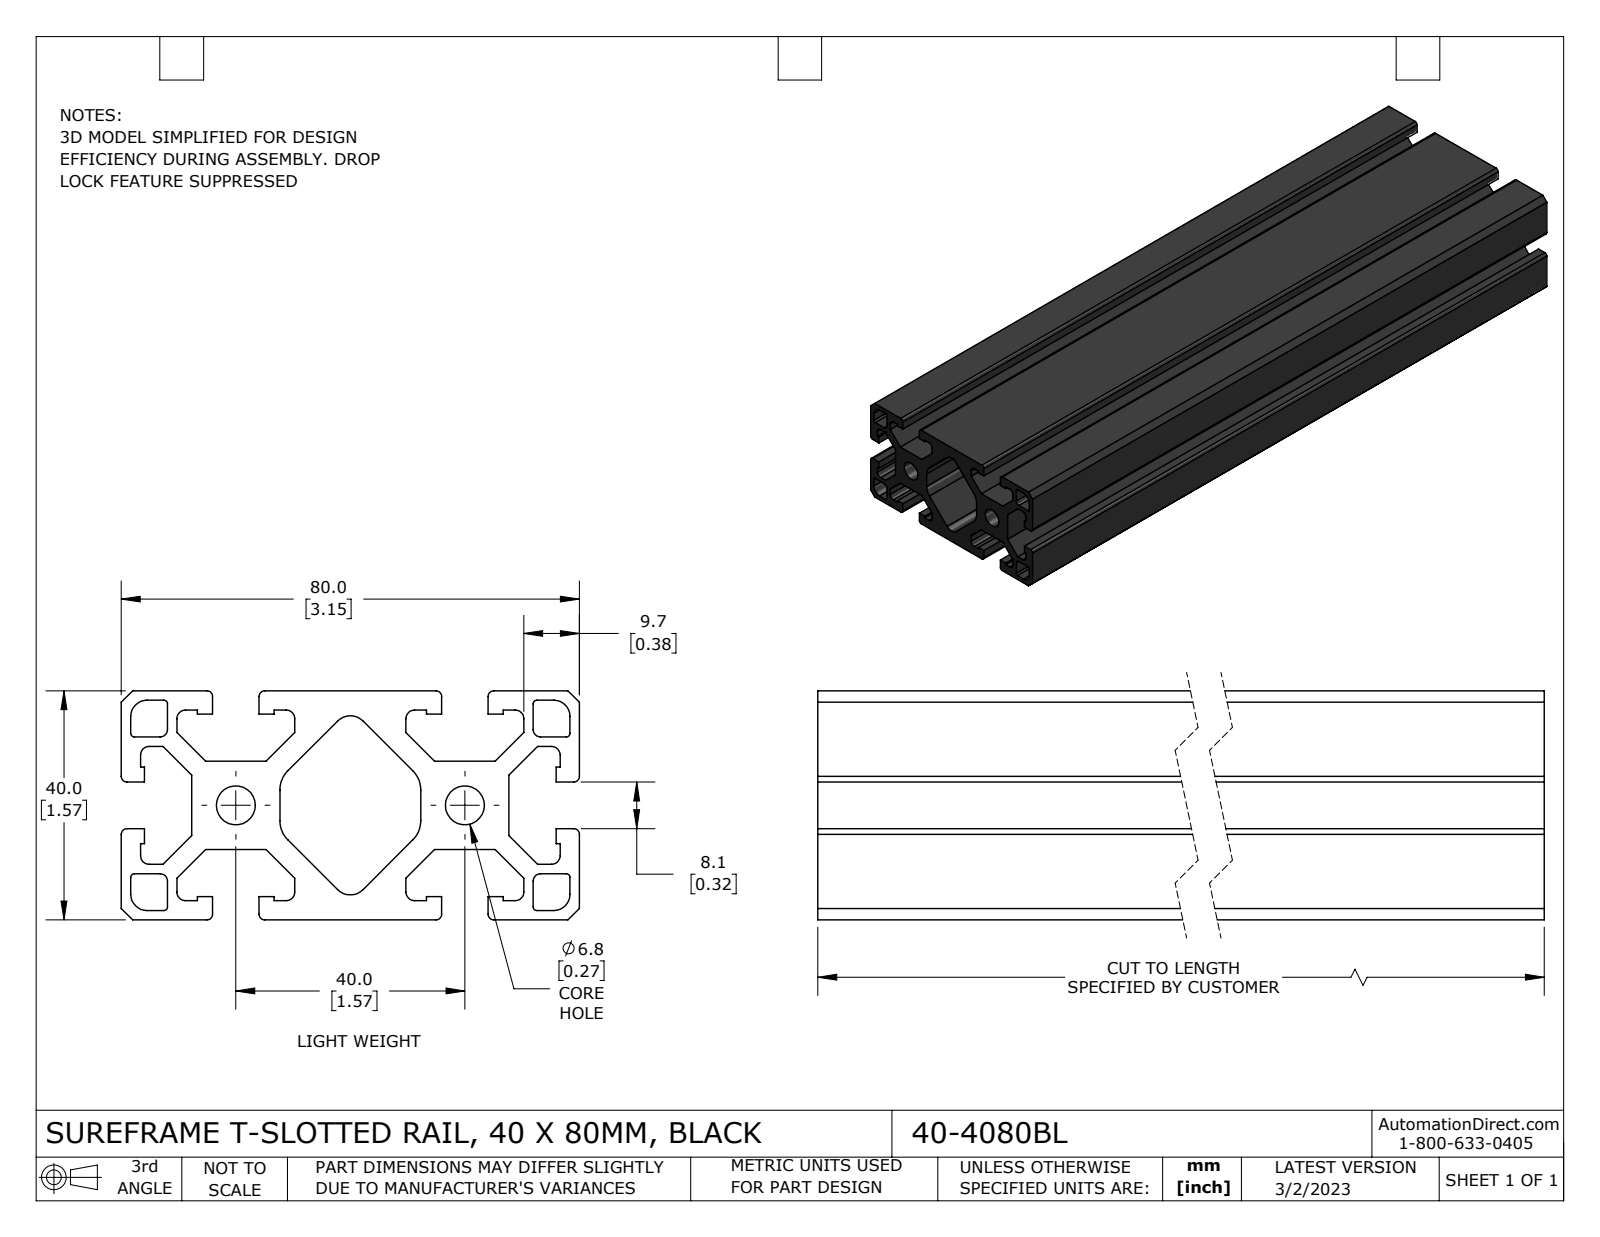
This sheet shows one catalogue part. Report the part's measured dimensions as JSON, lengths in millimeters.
{"part_name": "40-4080BL", "step_written_by": "SolidWorks 2021 (CONFIG_CONTROL_DESIGN)", "units": "millimeters", "bodies": {"solids": 1, "faces": 166, "planar": 116, "cylindrical": 50, "other": 0}, "overall_size": [254, 80, 40], "volume_mm3": 342238, "surface_area_mm2": 186010, "round_holes": [[6.81, 2]], "partial_cylinders_radius": [[1, 12], [1.5, 12], [0.63, 8], [1.27, 4], [2.8, 4], [4.75, 4], [3.17, 2]], "face_to_face_distances": [40, 12.3, 27.7, 3.87, 27.83, 11.76, 3.64, 8.06, 15.4, 4.06], "hole_center_spacings": [40]}
